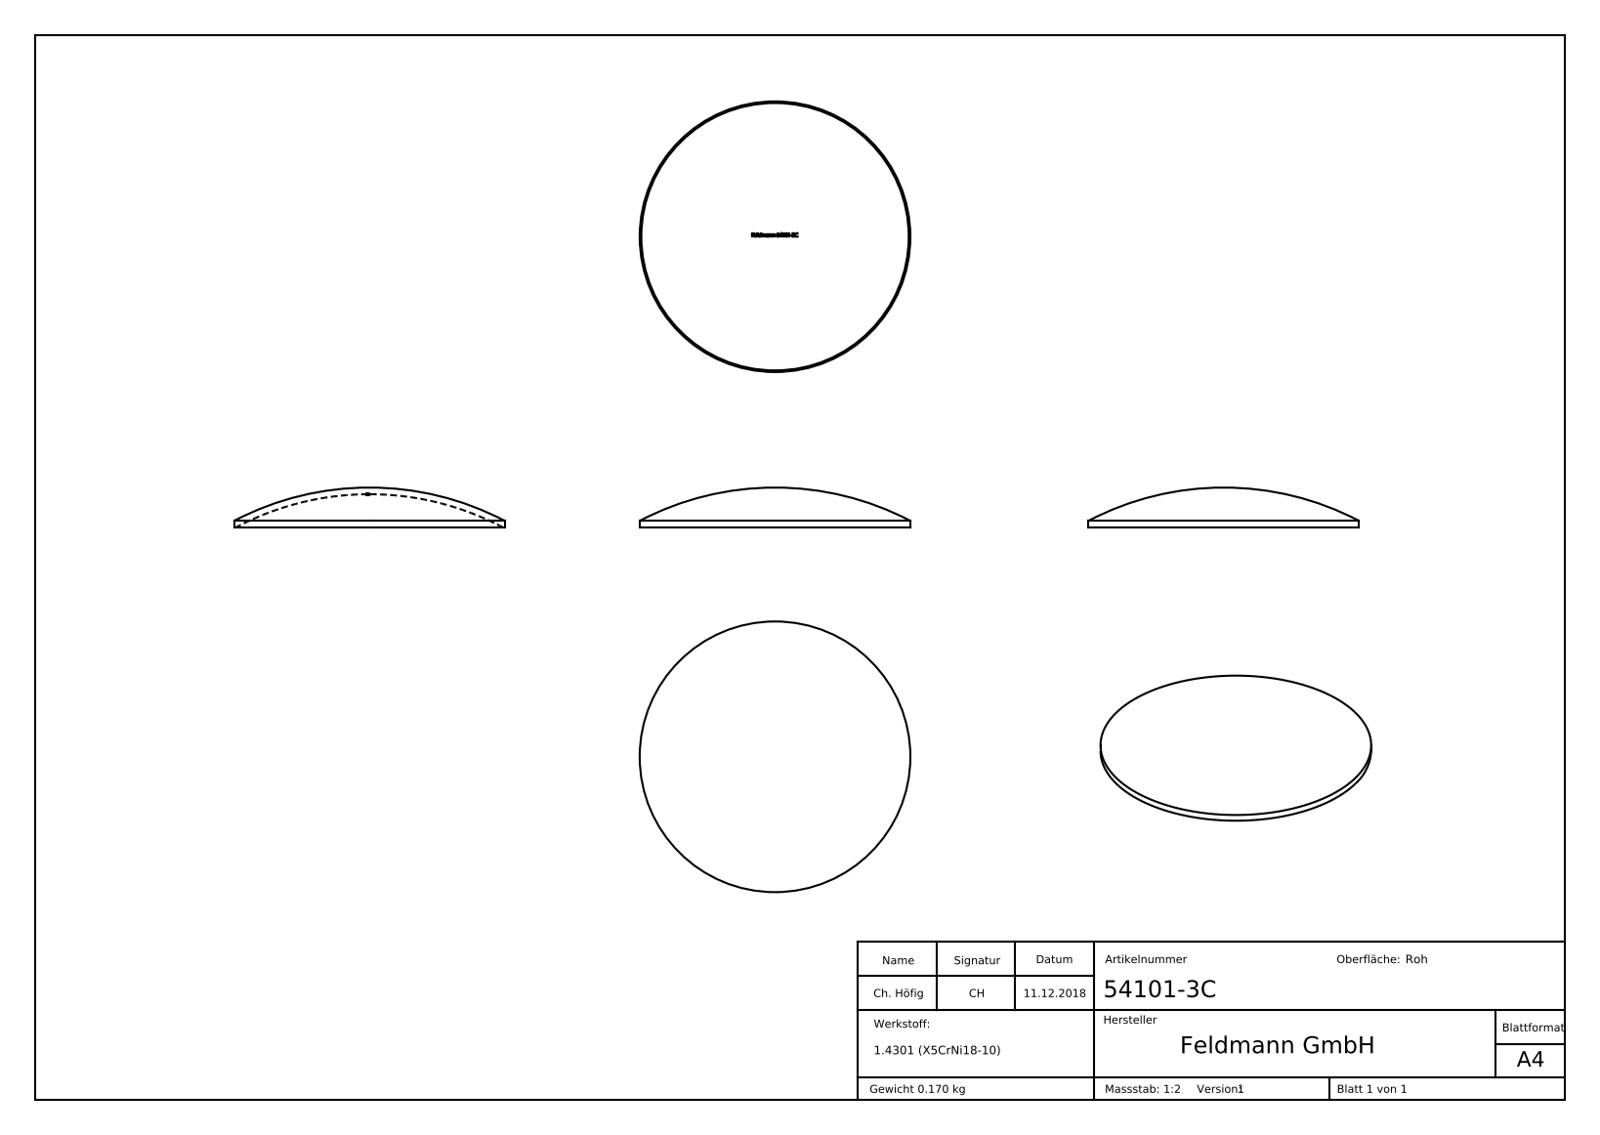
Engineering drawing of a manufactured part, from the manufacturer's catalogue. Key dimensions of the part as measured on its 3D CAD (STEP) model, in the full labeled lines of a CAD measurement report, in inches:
Part name (STEP PRODUCT): 54101-3C
STEP written by: SolidWorks 2015 (CONFIG_CONTROL_DESIGN)
Units: inches
Bodies: 1 solid, 223 faces (95 planar, 2 cylindrical, 126 other)
Overall size (bounding box): 4 × 4 × 0.591
Volume: 1.312 in³ · Surface area: 27.9 in²
Round bosses / shafts (diameter × count): ⌀4 ×1
Main face-to-face distances: 0.117, 0.015, 0.463, 0.08, 0.542, 0.049, 0.351, 0.111, 0.413, 0.065
